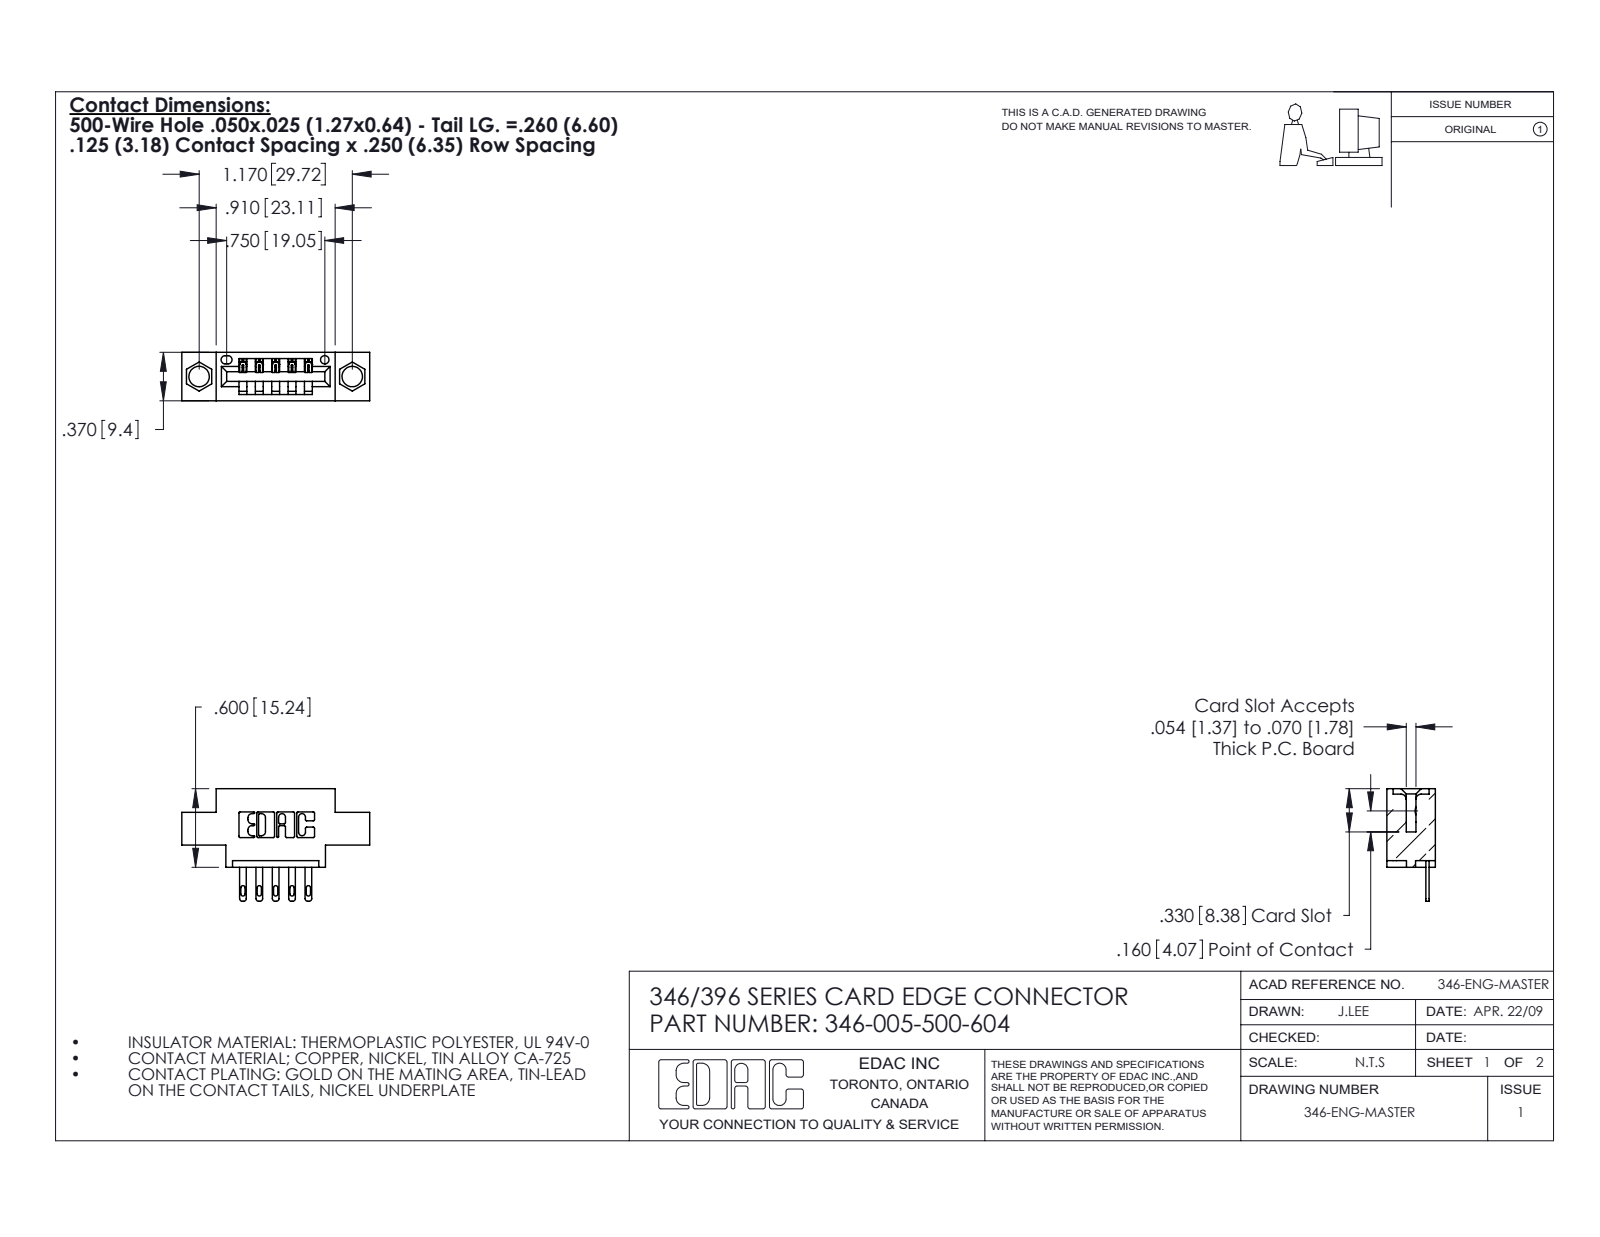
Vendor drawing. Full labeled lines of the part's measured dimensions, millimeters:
Part name (STEP PRODUCT): 346-005-500-604; 346 Part_0.170 Offset - 0.156 Dia-TH; 345-292-001_345-293-100
STEP written by: SolidWorks 2020 (CONFIG_CONTROL_DESIGN)
Units: millimetres
Bodies: 6 solids, 410 faces (264 planar, 146 cylindrical, 0 other)
Overall size (bounding box): 36.4 × 21.8 × 9.4
Volume: 2 980 mm³ · Surface area: 3 330 mm²
Round holes (diameter × count): ⌀4 ×2, ⌀1.6 ×1
Partial cylindrical surfaces — rounded edges, fillets, slot ends (radius × count): R0.3 ×22, R0.2 ×10, R0.4 ×10, R0.5 ×10, R0.2 ×6, R0.8 ×6, R0.7 ×3, R0.8 ×2
Main face-to-face distances: 6.4, 9.4, 1.2, 8.2, 5.6, 3.8, 2.5, 4.4, 1.8, 7.6
Hole centre spacings: 6.2, 24.6, 29.7
